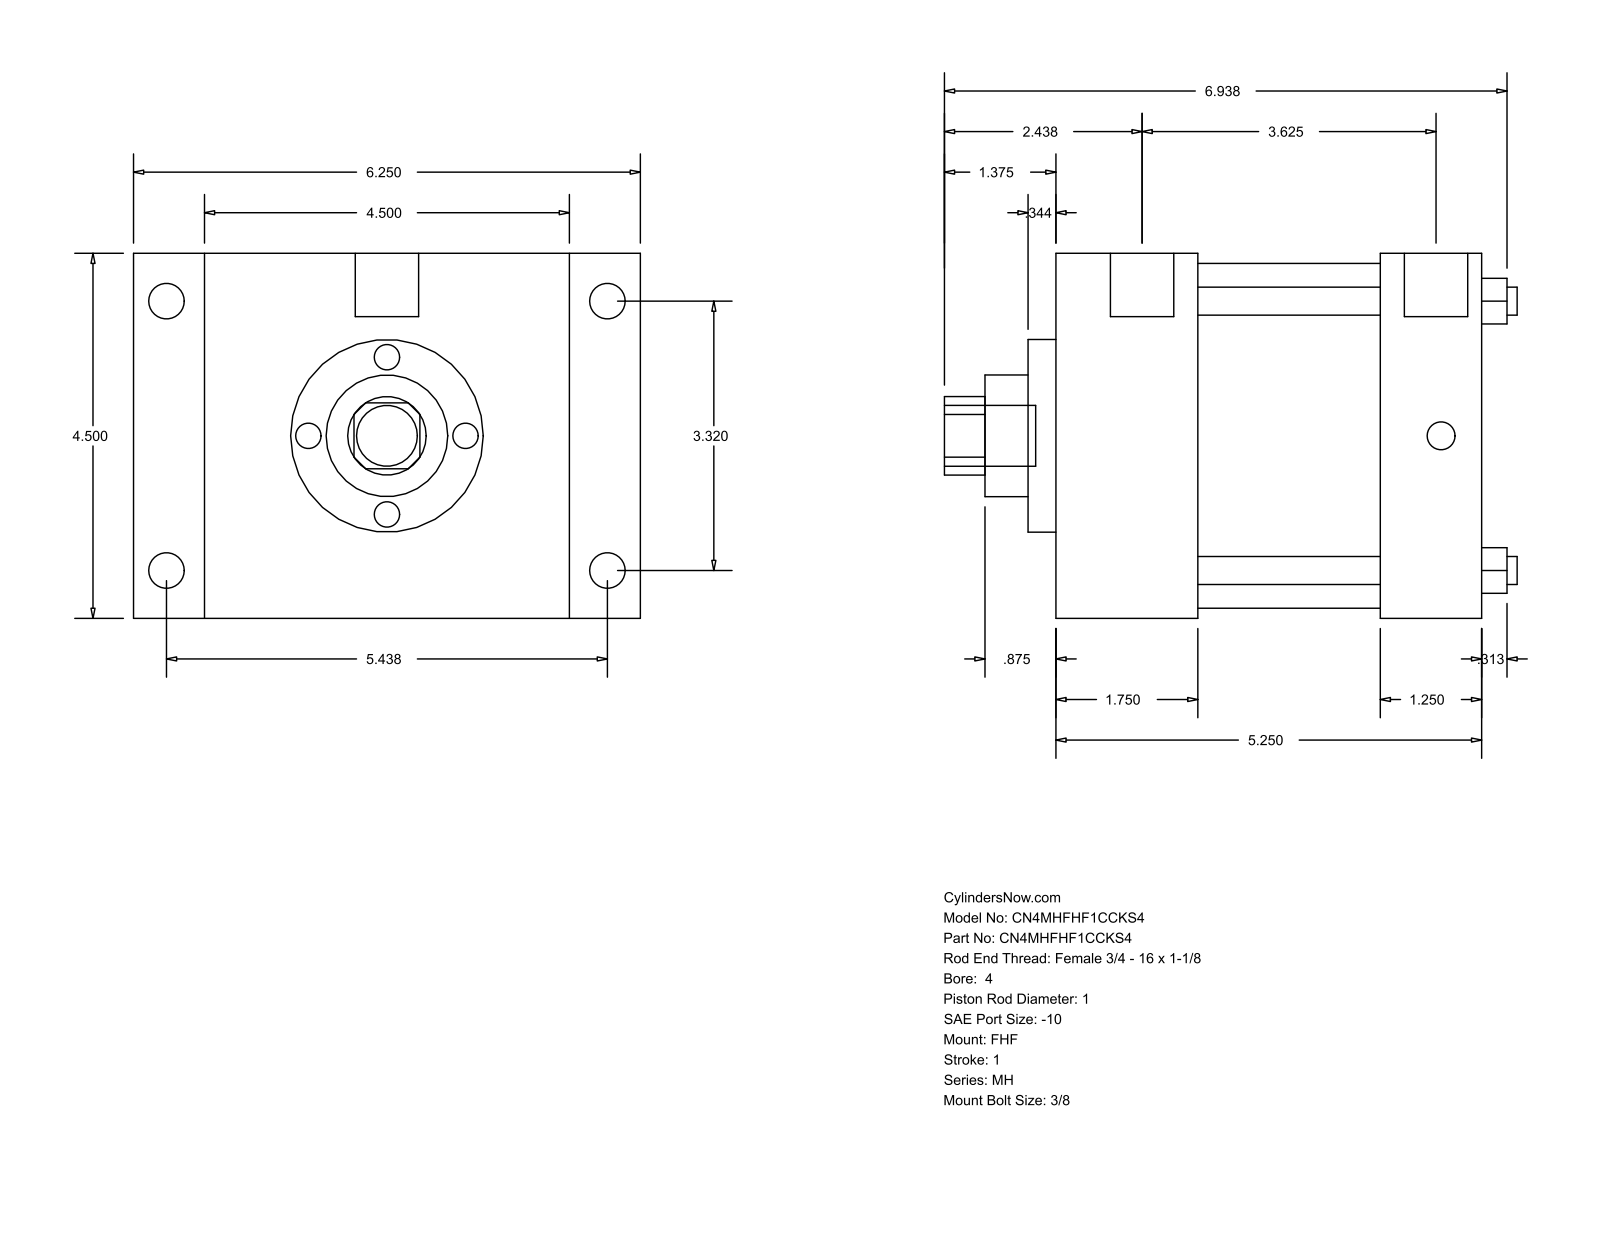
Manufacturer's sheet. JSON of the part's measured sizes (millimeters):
{"part_name": "MH_FHF__0400_1", "step_written_by": "GSSL Pune (CONFIG_CONTROL_DESIGN)", "units": "millimeters", "bodies": {"solids": 0, "faces": 90, "planar": 61, "cylindrical": 29, "other": 0}, "overall_size": [179.39, 158.75, 114.3], "round_holes": [[8.76, 4], [25.4, 1], [38.1, 1], [60.33, 1], [107.95, 1]], "round_bosses_or_shafts": [[11.13, 4], [8.73, 4], [19.84, 2], [19.05, 1]], "partial_cylinders_radius": [[12.29, 1]], "face_to_face_distances": [114.3, 133.36, 44.46, 88.9, 136.53, 22.23, 158.76, 101.61, 57.15, 31.75], "hole_center_spacings": [59.62, 84.32, 119.25]}
